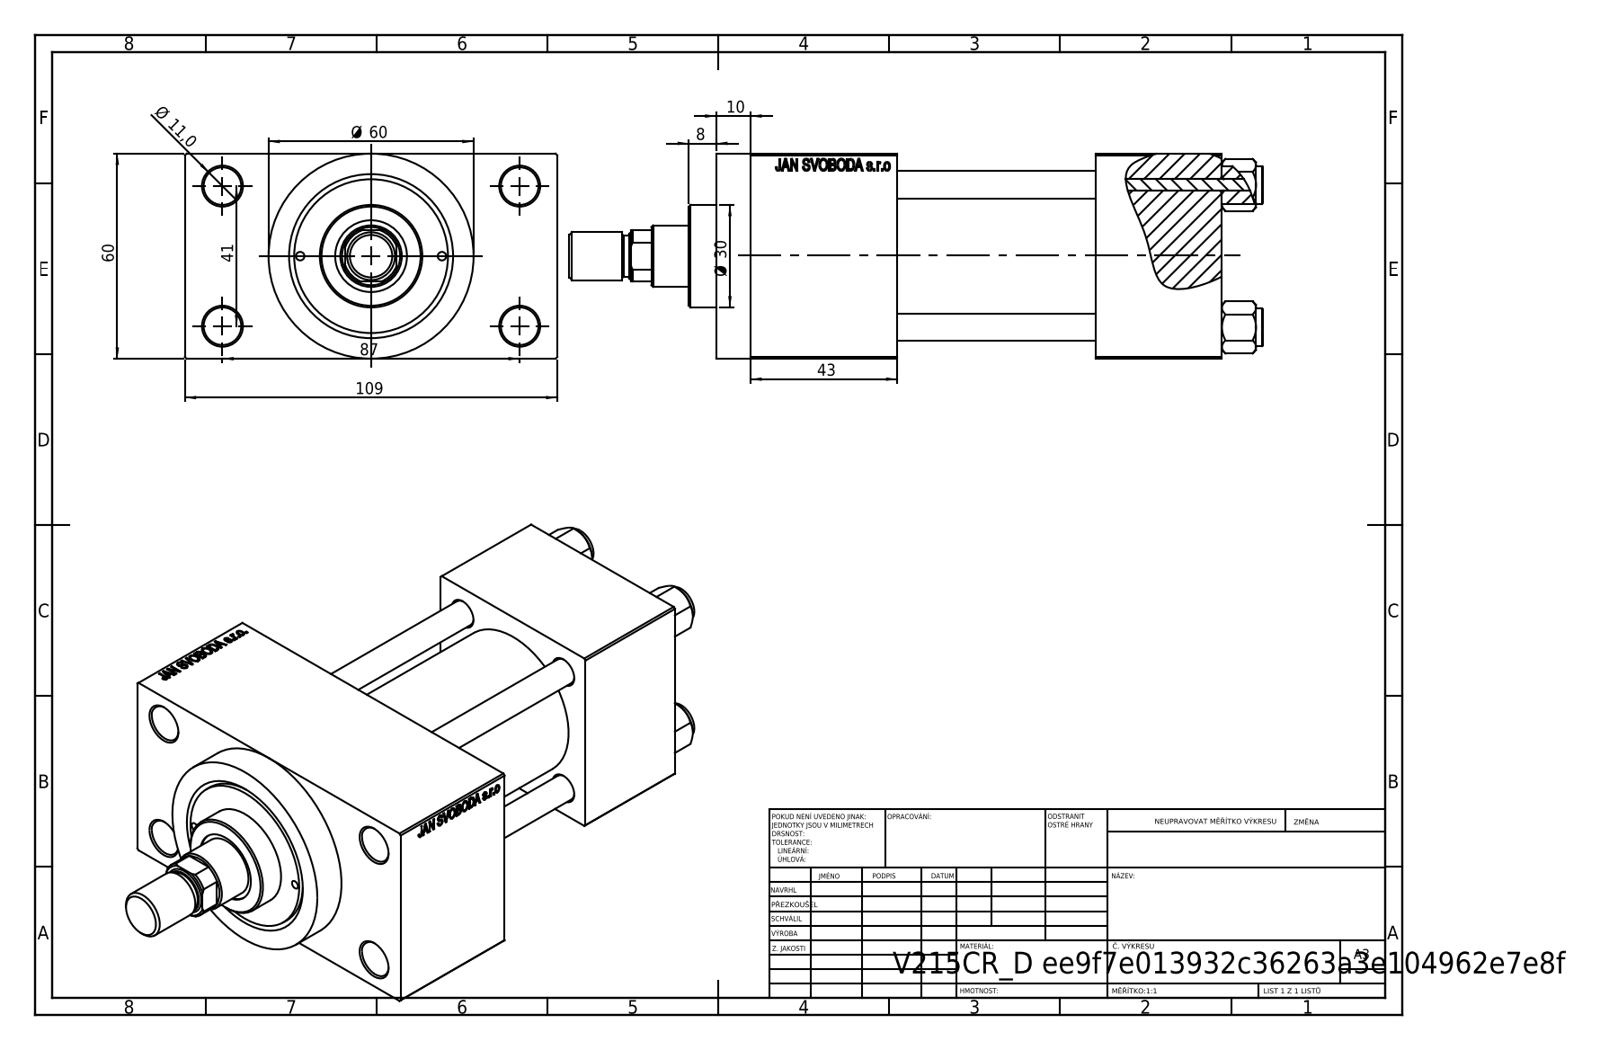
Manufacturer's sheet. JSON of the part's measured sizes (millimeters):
{"part_name": "NUT_M5_D; V215CR_VCP_D; V215CR_D_Body; V215CR_D_TYCINKA (+2 more)", "step_written_by": "SolidWorks 2019 (CONFIG_CONTROL_DESIGN)", "units": "millimeters", "bodies": {"solids": 12, "faces": 1127, "planar": 504, "cylindrical": 97, "other": 526}, "overall_size": [203, 109, 60], "volume_mm3": 520245, "surface_area_mm2": 122347, "round_holes": [[8, 4], [11, 4], [2.5, 2], [7, 2], [16.66, 2], [24, 2], [8.5, 1], [18, 1], [21, 1], [31, 1], [40, 1], [45, 1]], "round_bosses_or_shafts": [[11, 4], [60, 1], [46, 1], [30, 1], [14, 1], [12, 1]], "partial_cylinders_radius": [[8.5, 1]], "face_to_face_distances": [60, 24.5, 84.5, 58, 37, 95, 43, 138, 101, 109], "hole_center_spacings": [20.85, 22.65, 29.49, 30.62, 41.7, 46.53, 47.15, 48.09]}
